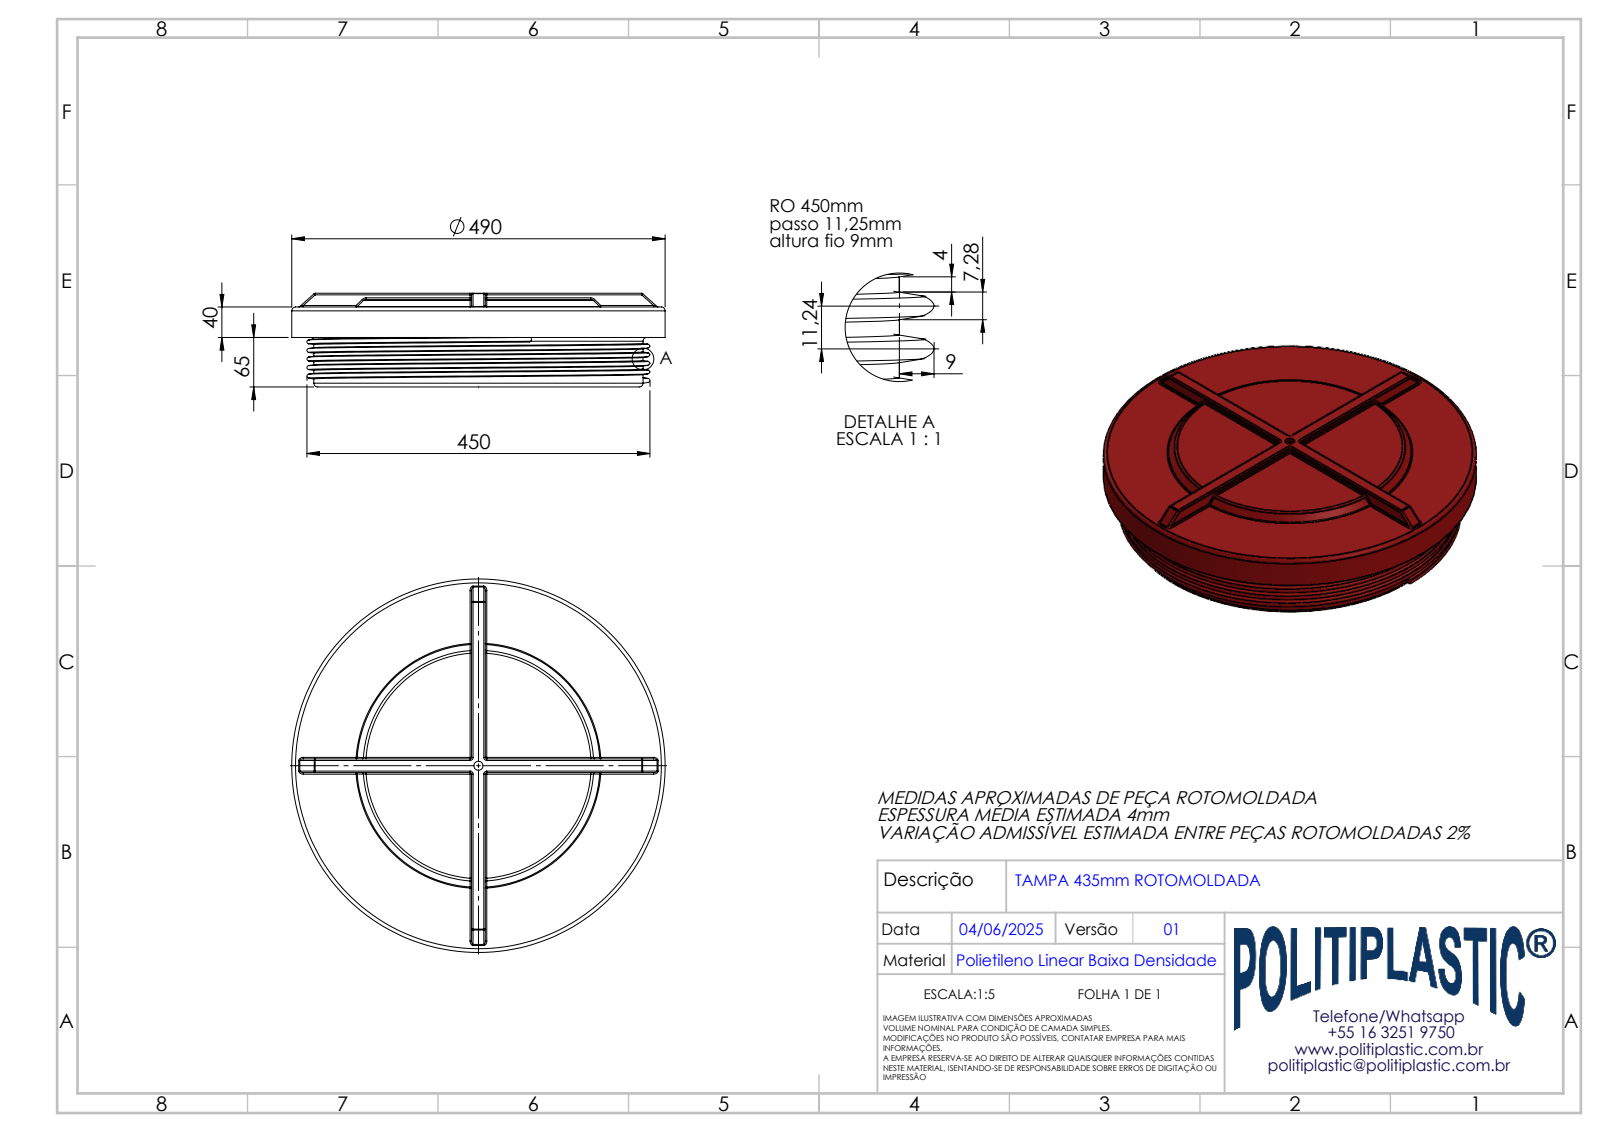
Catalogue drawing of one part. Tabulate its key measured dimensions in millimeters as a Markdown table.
| quantity | value |
| --- | --- |
| part name | TAMPA 435MM ROTOMOLDADA |
| STEP written by | SolidWorks 2025 (CONFIG_CONTROL_DESIGN) |
| units | millimeters |
| bodies | 1 solid, 247 faces (42 planar, 89 cylindrical, 116 other) |
| overall size | 490 × 490 × 123 |
| volume | 2 434 000 mm³ |
| surface area | 1 143 000 mm² |
| round holes (diameter × count) | 12 × 1, 424 × 1, 482 × 1 |
| round bosses / shafts (diameter × count) | 490 × 1, 432 × 1 |
| partial cylindrical surfaces (radius × count) | 2 × 32, 6 × 16 |
| main face-to-face distances | 4, 101, 10, 111, 105, 97, 14, 115, 65, 36 |
